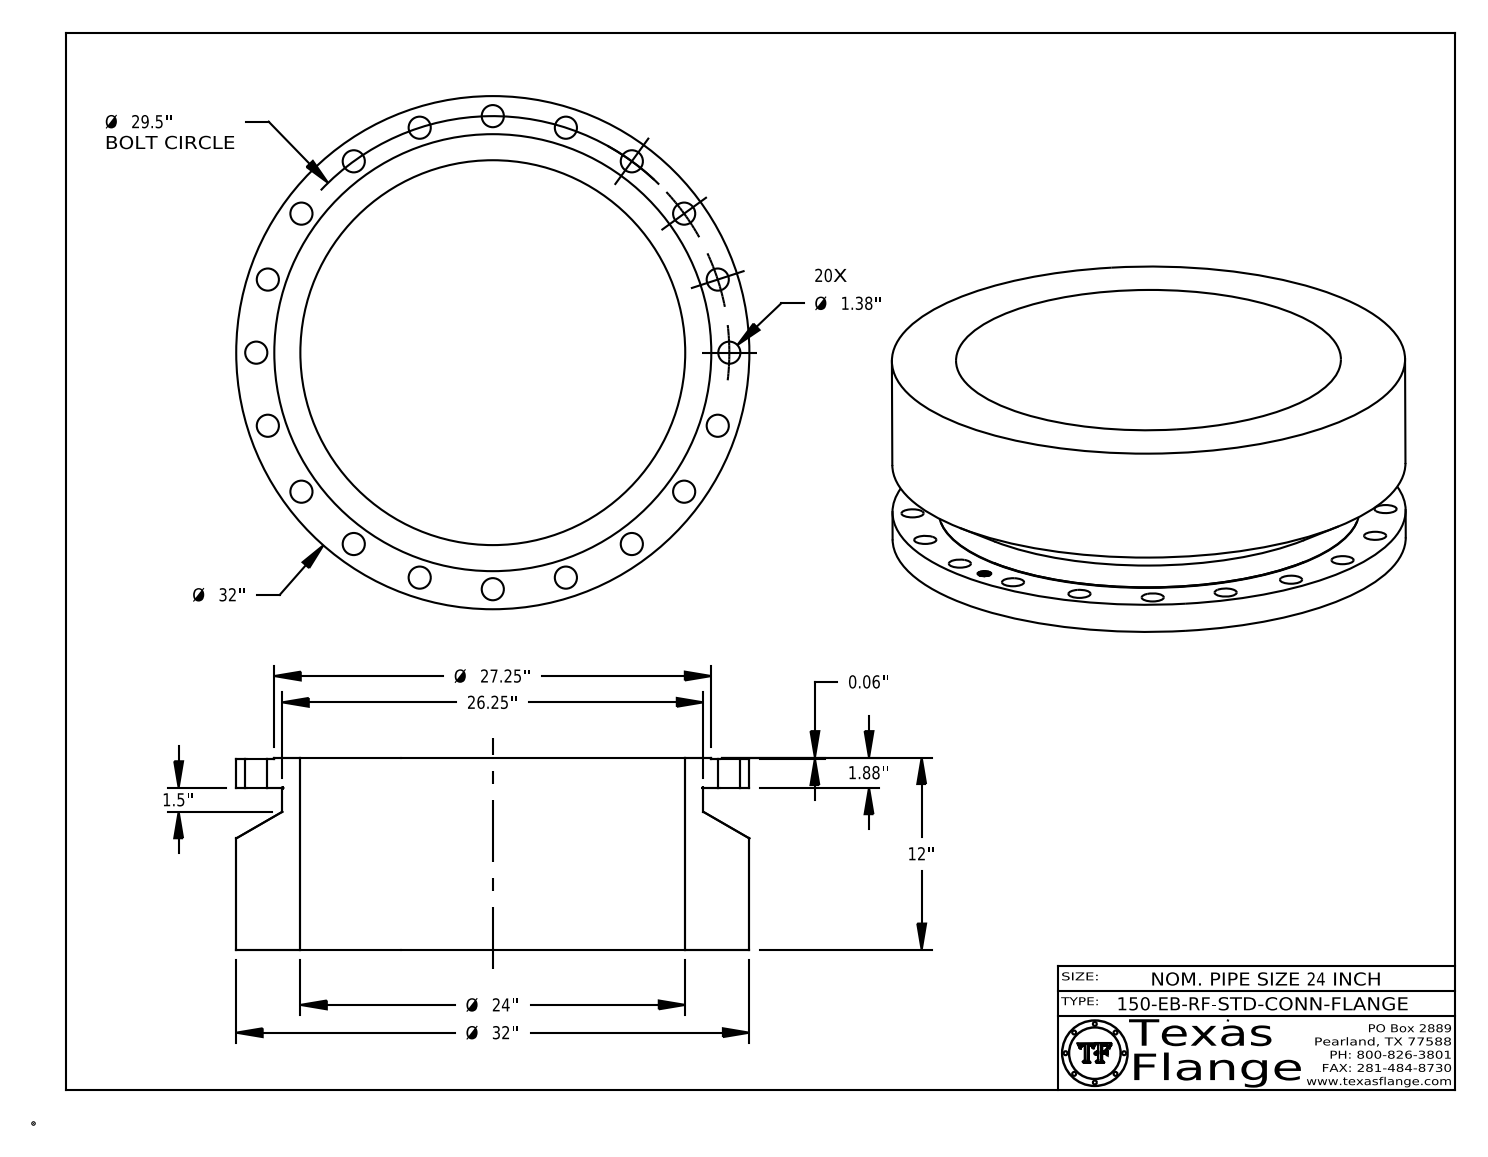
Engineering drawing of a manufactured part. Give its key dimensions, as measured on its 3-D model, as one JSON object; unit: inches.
{"part_name": "24-150-EB-RF-STD-CONN-FLANGE", "step_written_by": "CATIA V5 STEP AP214 (AUTOMOTIVE_DESIGN)", "units": "inches", "bodies": {"solids": 1, "faces": 445, "planar": 369, "cylindrical": 70, "other": 6}, "overall_size": [32, 32, 12], "volume_in3": 3534, "surface_area_in2": 3288, "round_holes": [[1.38, 20], [0.85, 1], [24, 1]], "round_bosses_or_shafts": [[0.051, 8], [32, 1], [27.25, 1], [26.25, 1], [0.67, 1]], "face_to_face_distances": [10.12, 1.817, 11.937, 0.063, 1.88, 12, 1.875, 1.813, 10.125, 0.254], "hole_center_spacings": [14.75, 29.137, 4.615, 17.34, 20.859, 23.866, 26.285, 9.116]}
